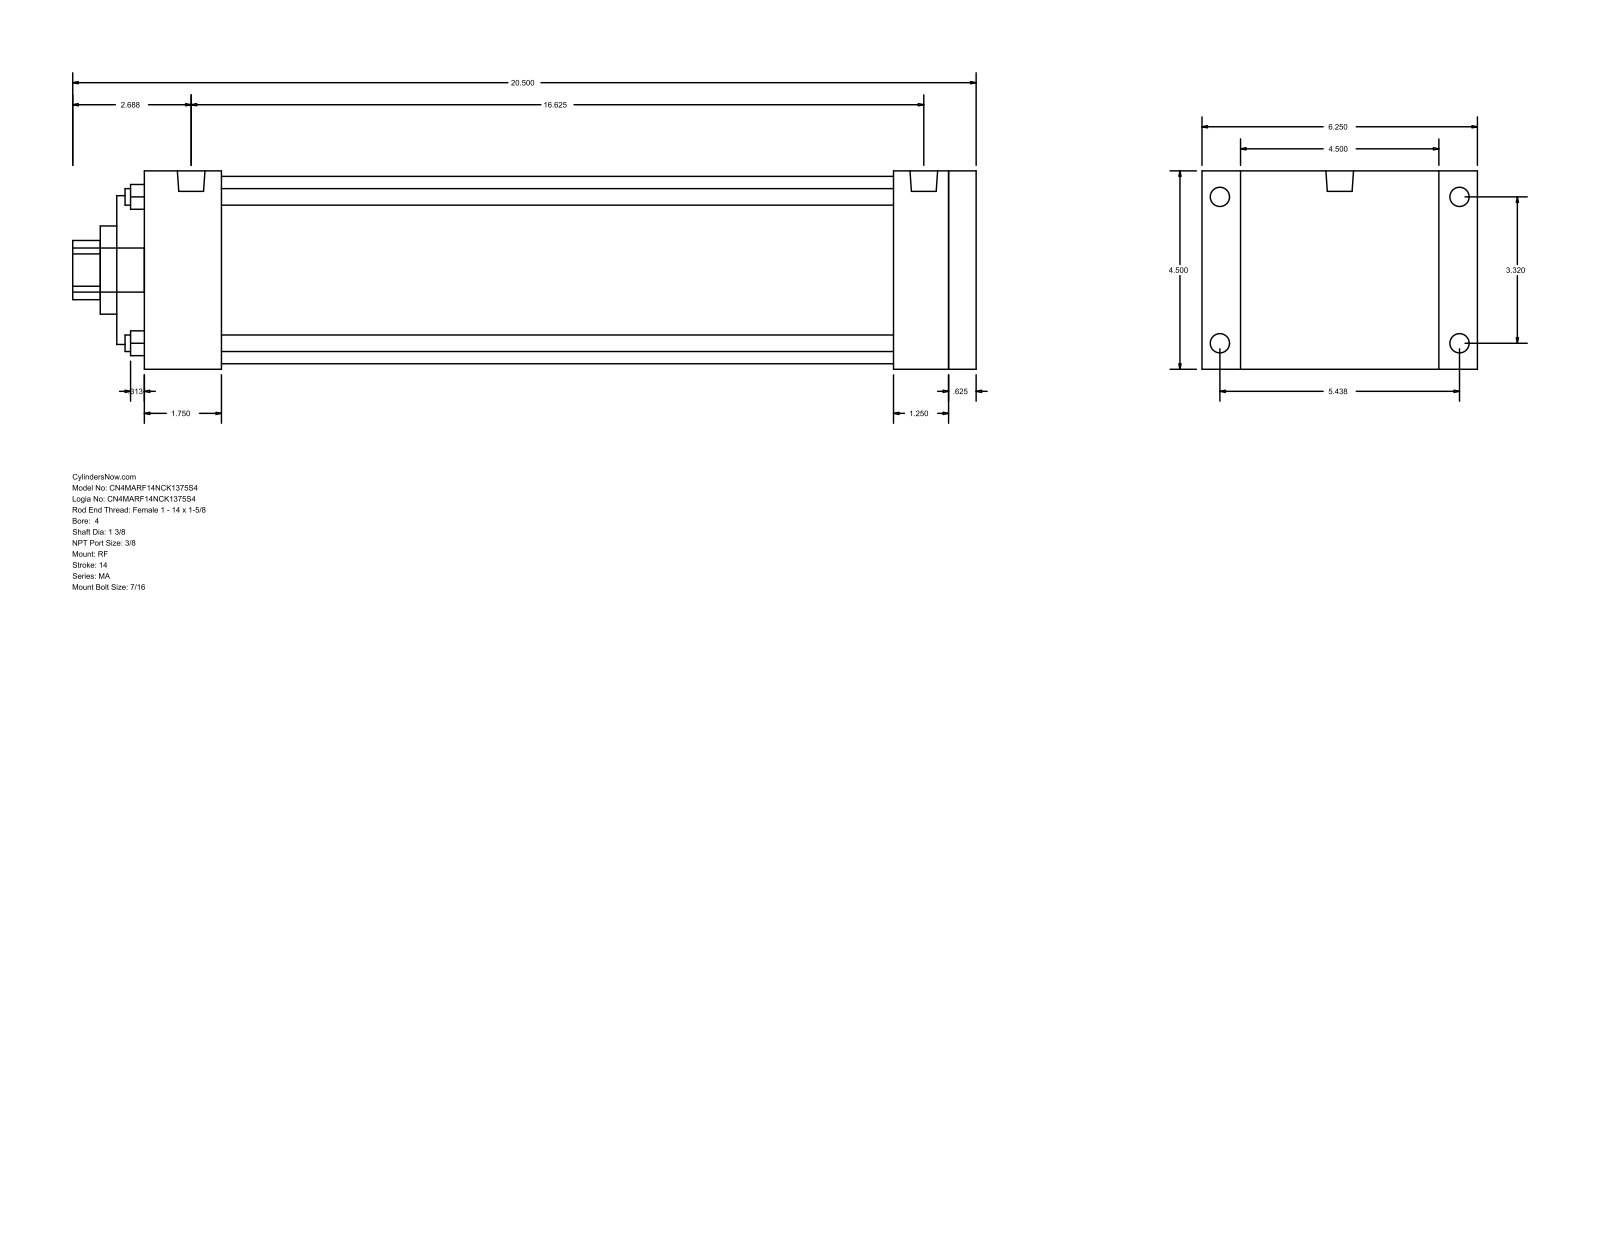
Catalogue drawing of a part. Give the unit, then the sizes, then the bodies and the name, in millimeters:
Units: millimetres
Overall size (bounding box): 520.7 × 158.75 × 114.3
Round holes (diameter × count): ⌀9.53 ×4, ⌀34.92 ×1, ⌀50.8 ×1, ⌀85.72 ×1, ⌀107.95 ×1
Round bosses / shafts (diameter × count): ⌀11.11 ×8, ⌀15.93 ×2, ⌀25.4 ×1
Partial cylindrical surfaces — rounded edges, fillets, slot ends (radius × count): R17.06 ×1
Main face-to-face distances: 114.3, 479.43, 15.88, 463.55, 15.87, 479.42, 495.3, 22.23, 136.53, 447.67
Hole centre spacings: 59.62, 84.32, 119.25
Bodies: 0 solids, 94 faces (65 planar, 29 cylindrical, 0 other)
Part name (STEP PRODUCT): MA_RF__0400_1.375
STEP written by: GSSL Pune (CONFIG_CONTROL_DESIGN)
